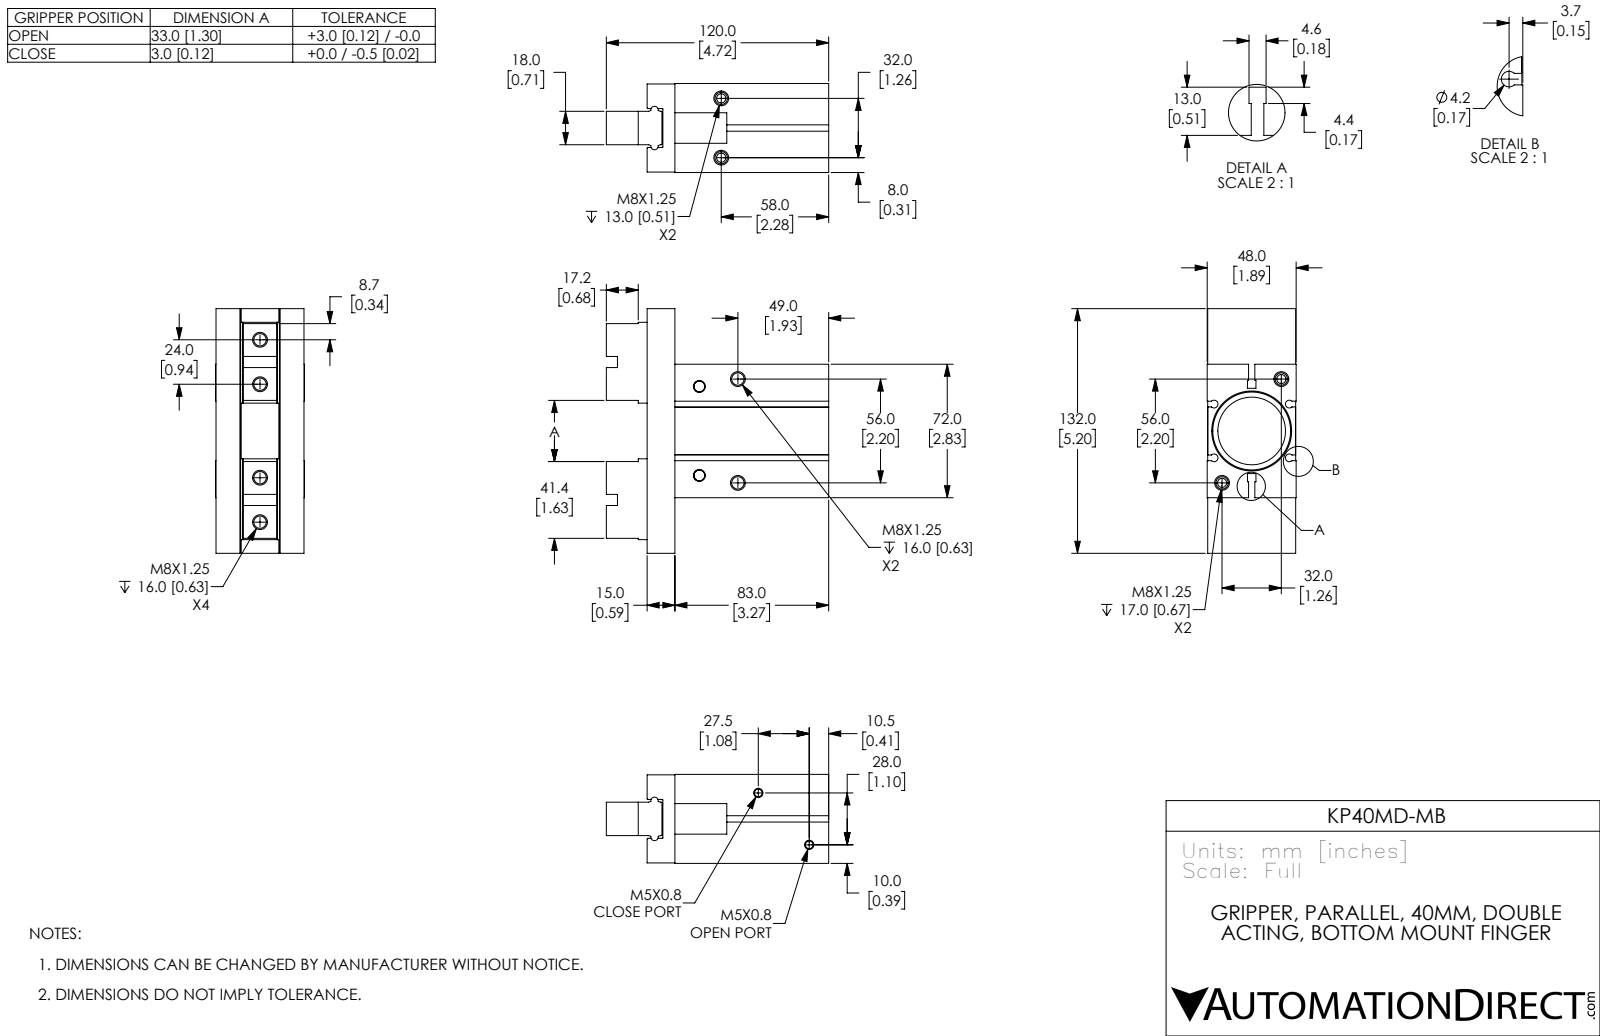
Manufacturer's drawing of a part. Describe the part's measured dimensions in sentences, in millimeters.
The part is named "KP40MD-MB; KP40MD-MB-3; KP40MD-MB-2; KP40MD-MB-1". Its 3-D file was written by "SolidWorks 2017 (CONFIG_CONTROL_DESIGN)". It is 3 solids with 243 faces: 126 planar, 63 cylindrical and 54 other. Overall it measures 132 by 120 by 48 millimeters. Its volume is 342 112 cubic millimeters and its surface area 68 141 square millimeters. Round holes: 10 of diameter 6.65, 2 of diameter 0.5, 2 of diameter 4.13, 2 of diameter 8.02, 1 of diameter 36.5, 1 of diameter 42. Partial cylindrical surfaces (rounded edges, fillets, slot ends): 7 of radius 0.2, 4 of radius 2.1, 2 of radius 0.3, 2 of radius 2. The main face-to-face distances are 15, 47.7, 33, 15.75, 32.25, 15.45, 31.95, 47.75, 15.5, 32. The hole center spacings are 16.24, 24, 25.2, 26.56, 32.25, 49.2, 55.55, 74.4.
